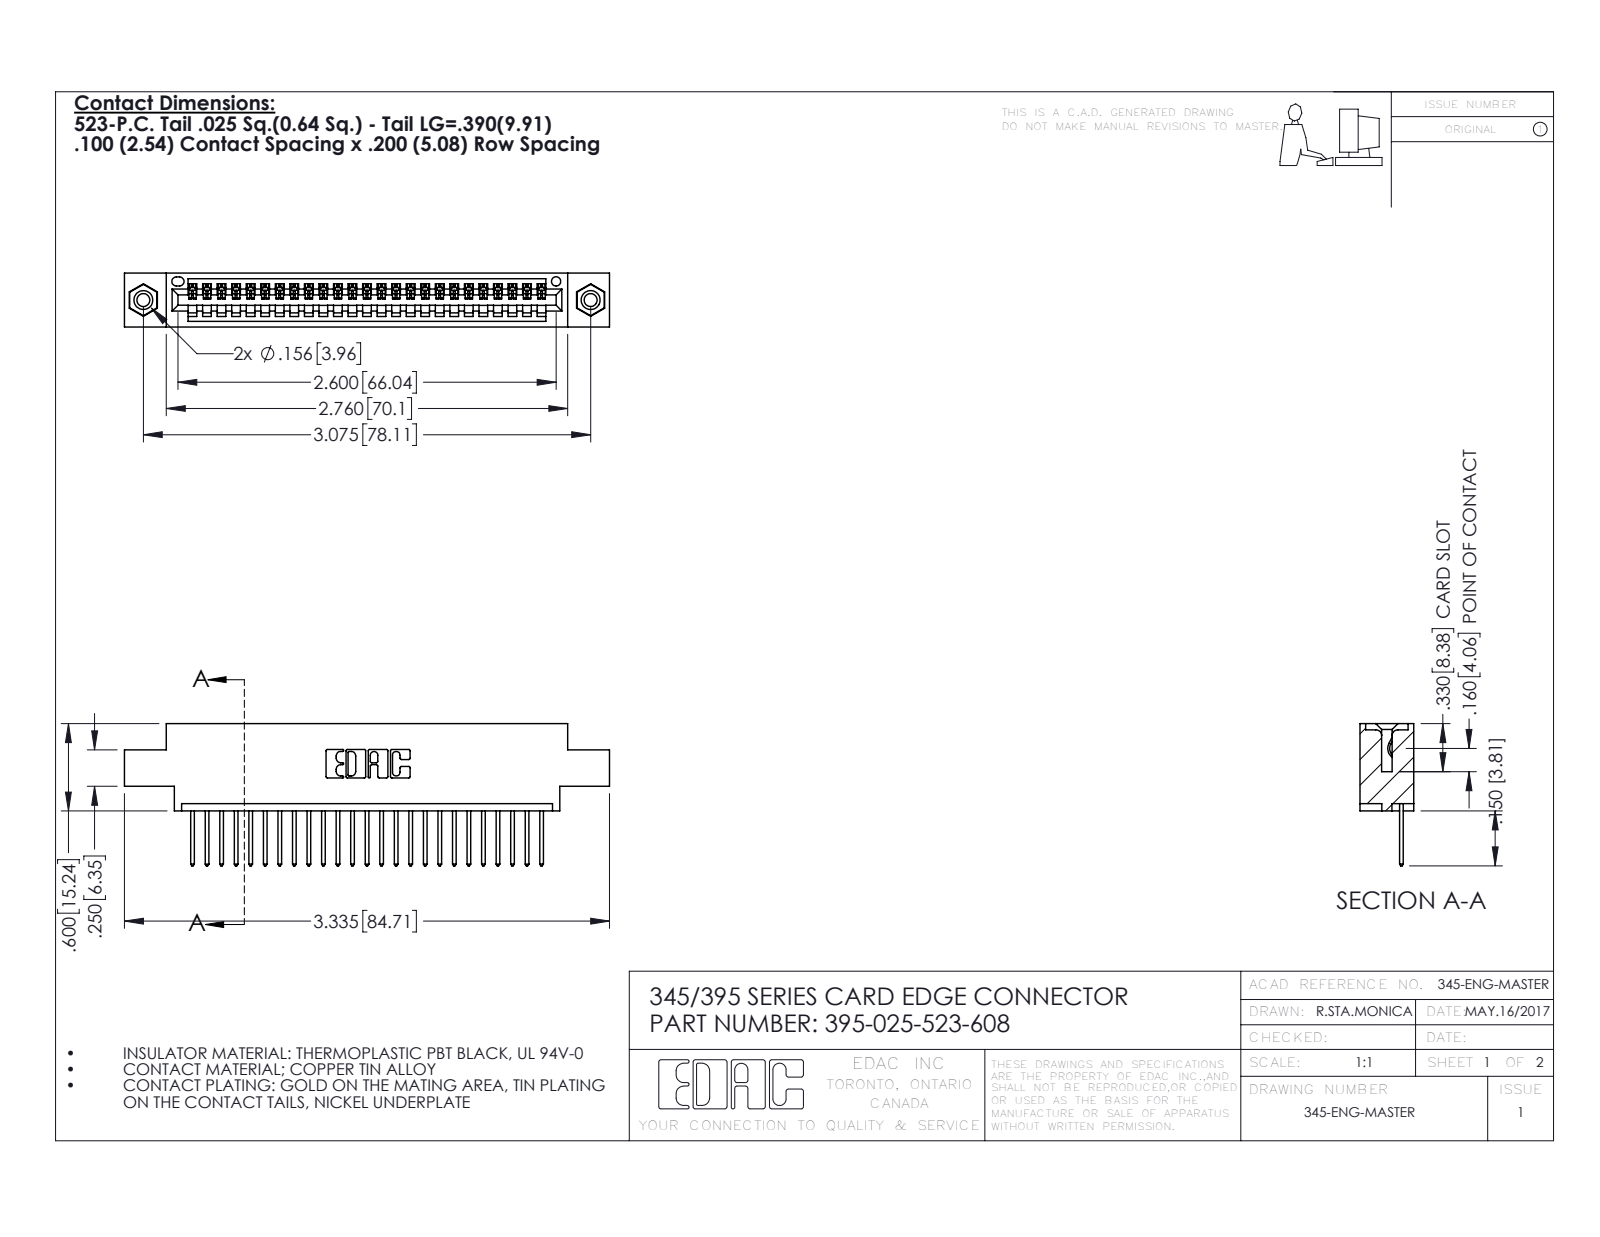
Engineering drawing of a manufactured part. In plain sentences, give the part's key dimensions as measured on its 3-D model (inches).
The part is named "345-250-001_345-250-003-102; 345-292-001_345-293-123; 345 Part_0.170 Offset - 0.156 Dia-TI; 395-025-523-608". Its 3-D file was written by "SolidWorks 2016 (CONFIG_CONTROL_DESIGN)". It is 28 solids with 1640 faces: 1116 planar, 508 cylindrical and 16 other. Overall it measures 3.335 by 0.977 by 0.37 inches. Its volume is 0.475 cubic inches and its surface area 15.93 square inches. Round holes: 2 of diameter 0.089, 2 of diameter 0.125, 2 of diameter 0.156, 1 of diameter 0.064. Round bosses or shafts: 2 of diameter 0.155. Partial cylindrical surfaces (rounded edges, fillets, slot ends): 50 of radius 0.006, 50 of radius 0.01, 22 of radius 0.01, 6 of radius 0.007, 6 of radius 0.031, 3 of radius 0.026, 2 of radius 0.031, 2 of radius 0.04. The main face-to-face distances are 0.072, 0.298, 0.37, 0.2, 0.098, 0.272, 0.025, 0.225, 0.175, 0.149. The hole center spacings are 0.27, 2.84, 3.075.
